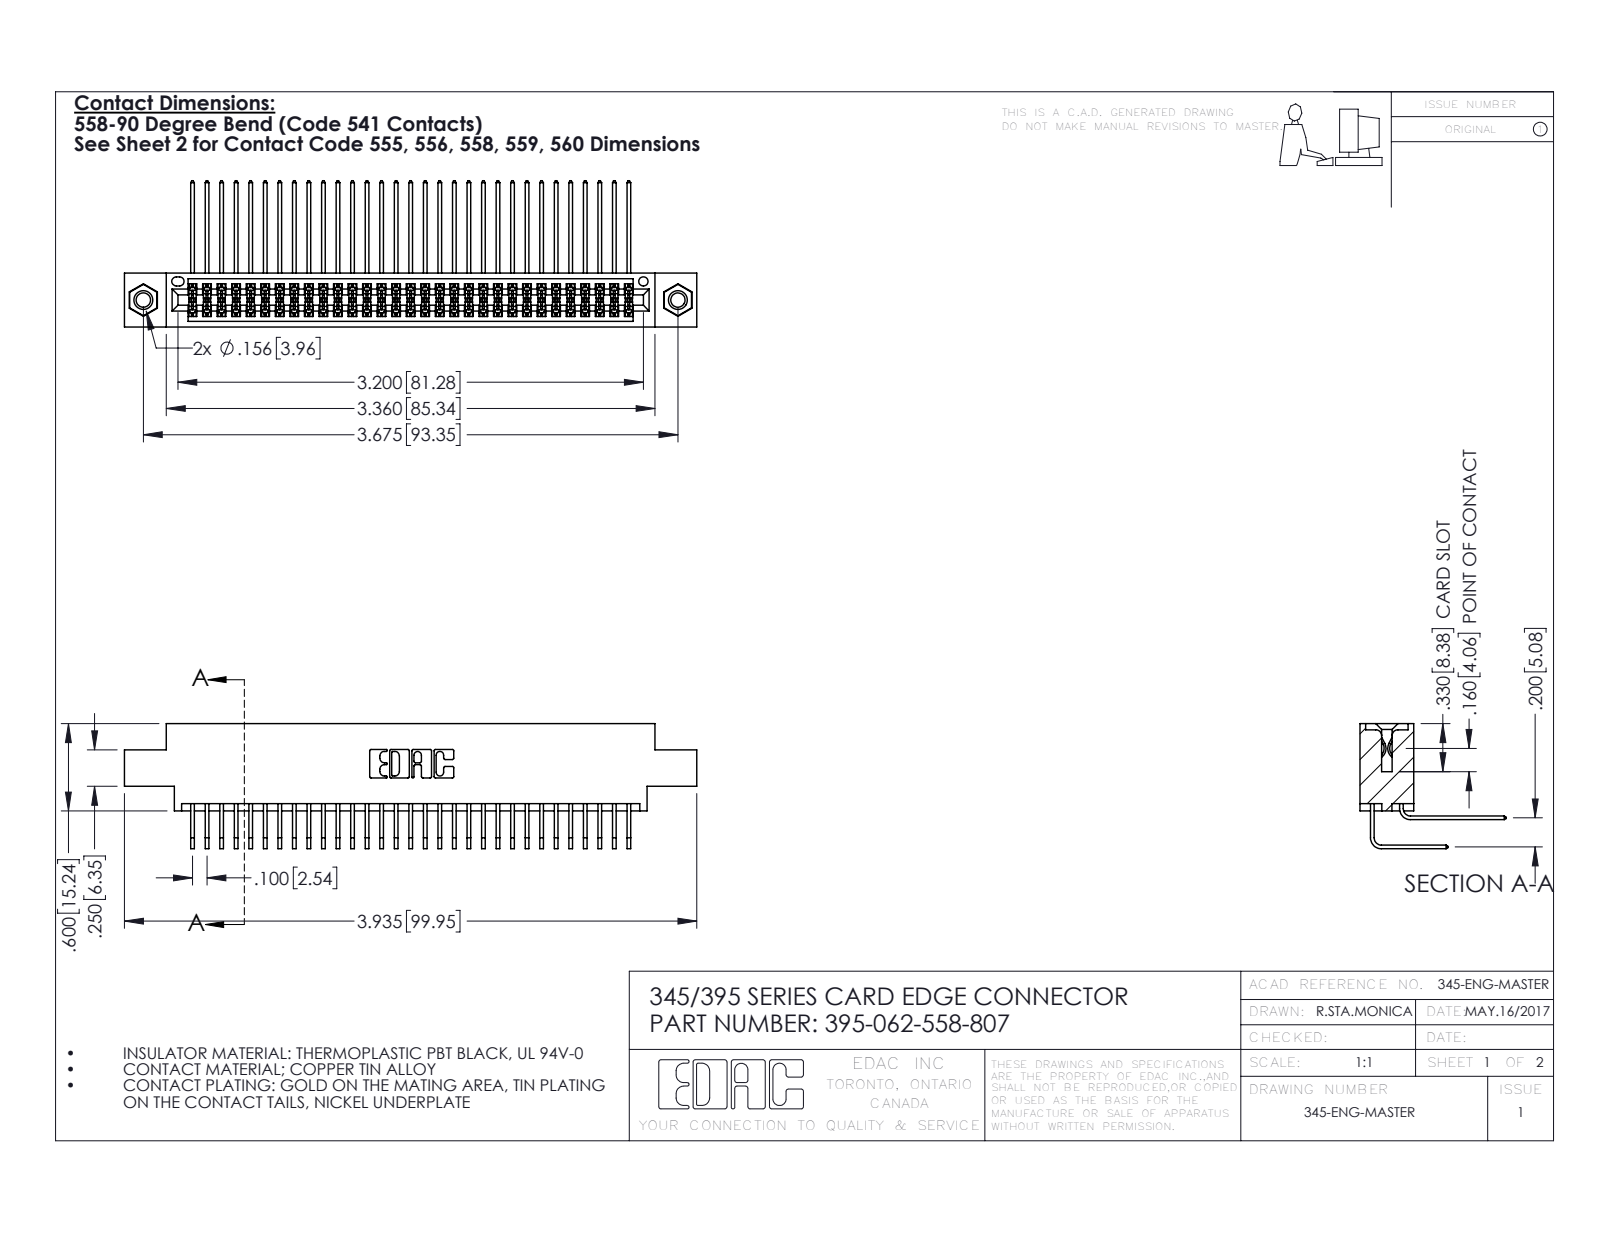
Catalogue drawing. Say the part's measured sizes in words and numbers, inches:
The part is named "395-062-558-807; 345 Part_0.170 Offset - 0.156 Dia-TI; 345-250-001_345-250-005-103; 345-292-001_558 Tail - 2 (+1 more)". Its 3-D file was written by "SolidWorks 2016 (CONFIG_CONTROL_DESIGN)". It is 65 solids with 3414 faces: 2286 planar, 1112 cylindrical and 16 other. Overall it measures 3.935 by 1.005 by 0.859 inches. Its volume is 0.6 cubic inches and its surface area 25.08 square inches. Round holes: 2 of diameter 0.098, 2 of diameter 0.125, 2 of diameter 0.156, 1 of diameter 0.064. Round bosses or shafts: 2 of diameter 0.155. Partial cylindrical surfaces (rounded edges, fillets, slot ends): 94 of radius 0.006, 22 of radius 0.01, 6 of radius 0.007, 6 of radius 0.031, 3 of radius 0.026, 2 of radius 0.014, 2 of radius 0.019, 2 of radius 0.022. The main face-to-face distances are 0.072, 0.298, 0.2, 0.37, 0.098, 0.272, 0.025, 0.225, 0.175, 0.025. The hole center spacings are 0.27, 3.44, 3.675.
